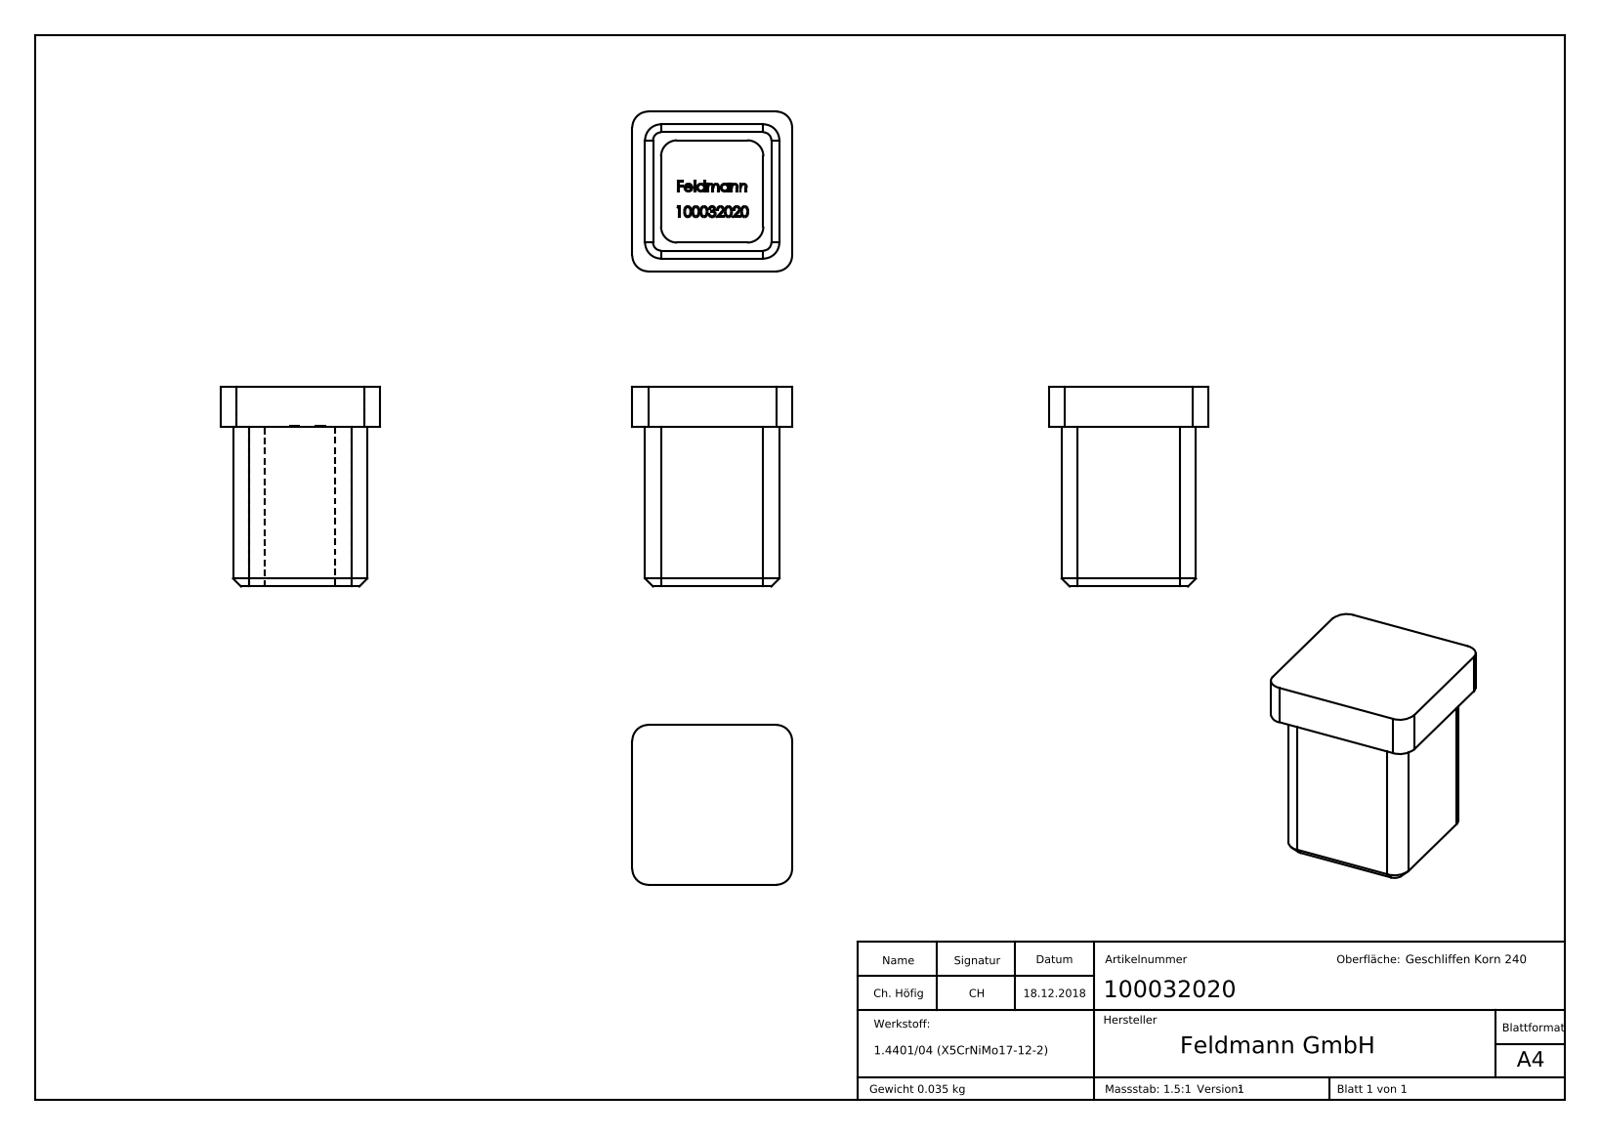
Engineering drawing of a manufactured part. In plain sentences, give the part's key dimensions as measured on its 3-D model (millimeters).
The part is named "100032020". Its 3-D file was written by "SolidWorks 2015 (CONFIG_CONTROL_DESIGN)". It is 1 solid with 255 faces: 120 planar, 12 cylindrical and 123 other. Overall it measures 60 by 60 by 25 millimeters. Its volume is 26 481 cubic millimeters and its surface area 16 727 square millimeters. Partial cylindrical surfaces (rounded edges, fillets, slot ends): 12 of radius 2. The main face-to-face distances are 2, 53.8, 5, 55.8, 51.8, 2.1, 4.1, 55.9, 57.9, 60.
